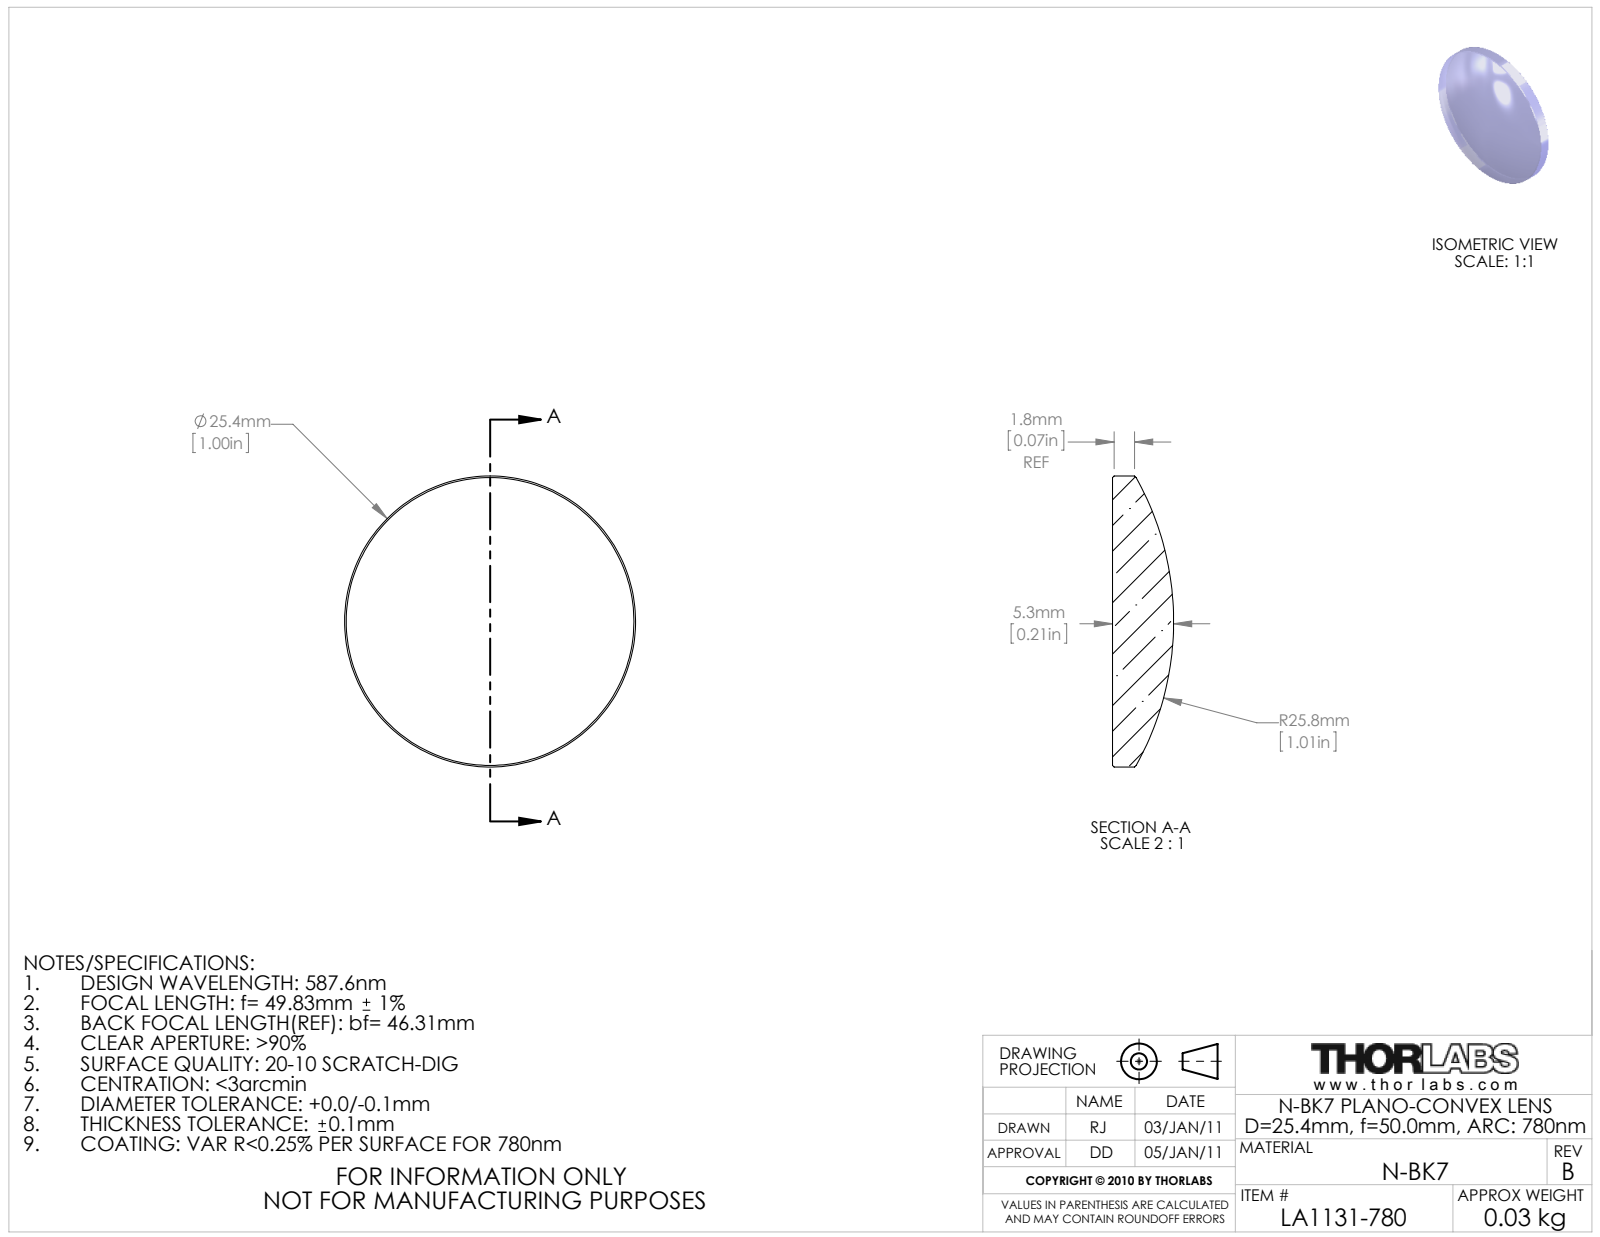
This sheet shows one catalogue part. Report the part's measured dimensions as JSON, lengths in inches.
{"part_name": "21787-E0W", "step_written_by": "SolidWorks 2011 (AUTOMOTIVE_DESIGN)", "units": "inches", "bodies": {"solids": 0, "faces": 9, "planar": 1, "cylindrical": 2, "other": 6}, "overall_size": [1, 1, 0.21], "round_bosses_or_shafts": [[1, 1]]}
